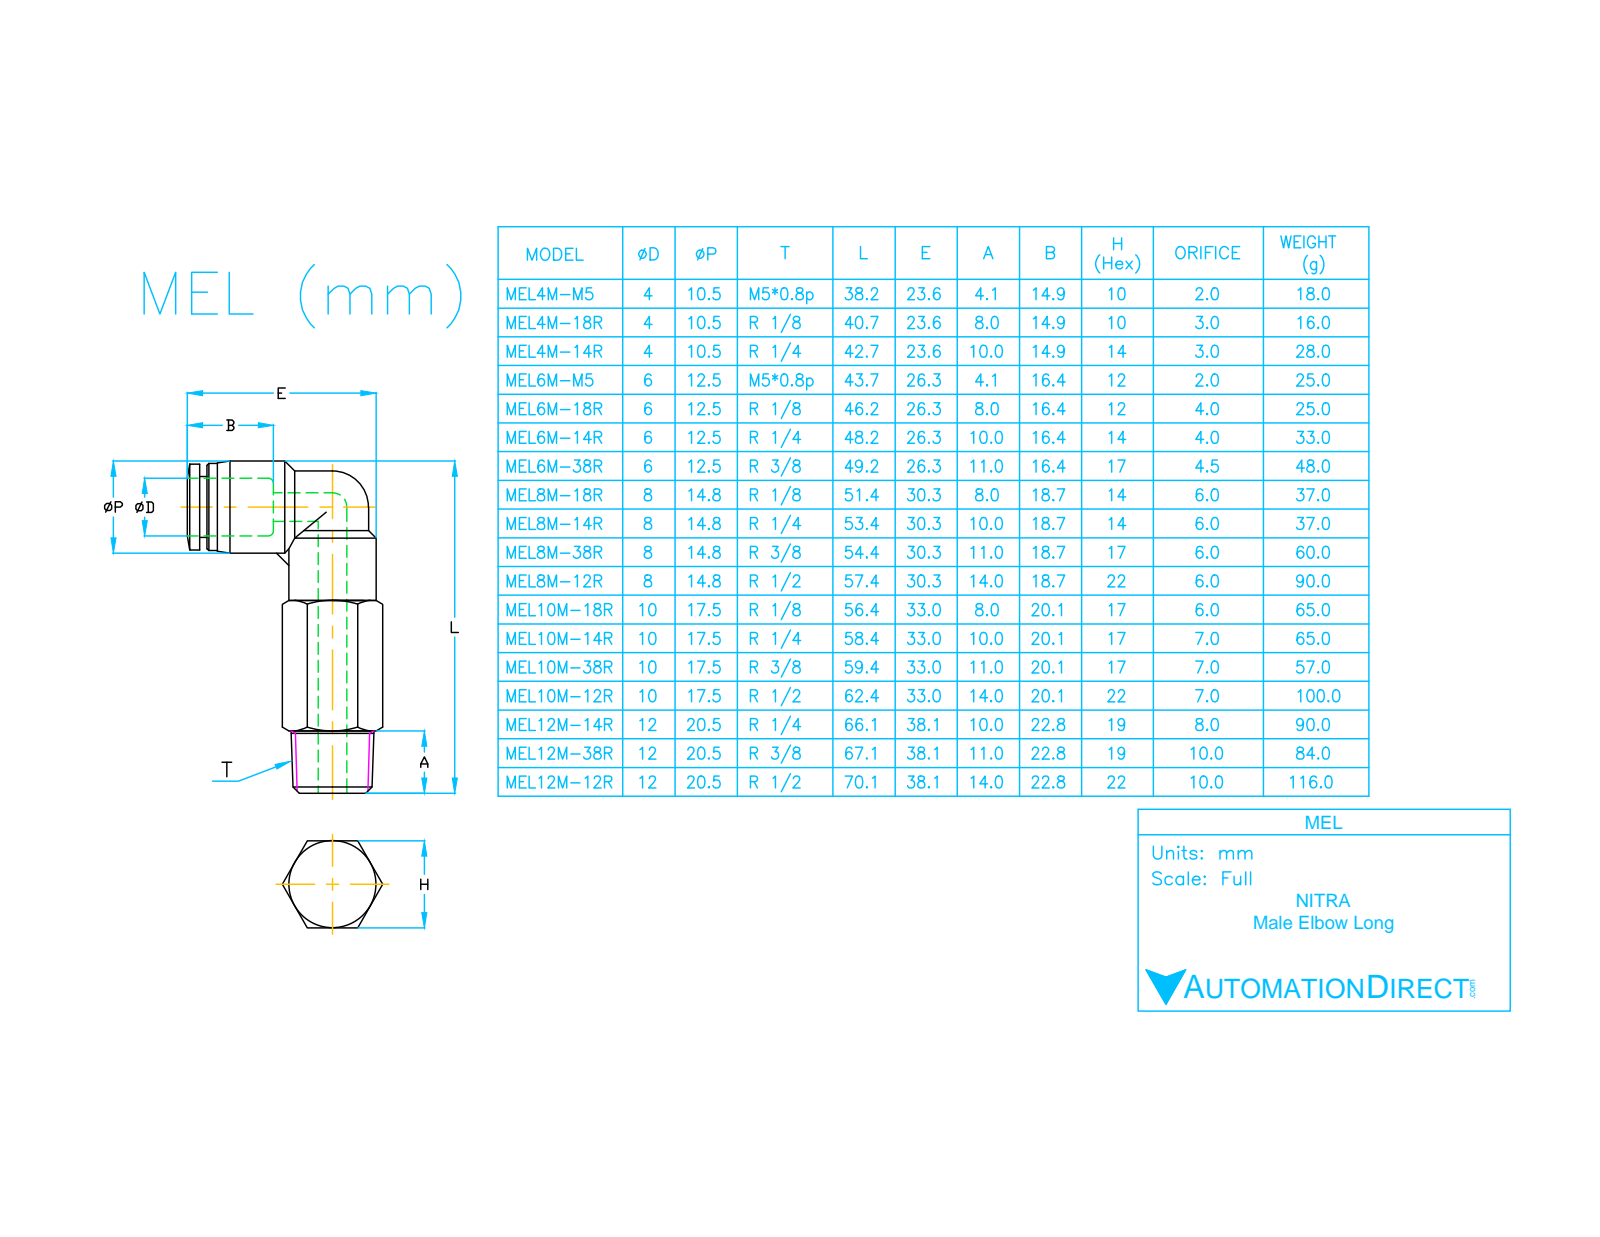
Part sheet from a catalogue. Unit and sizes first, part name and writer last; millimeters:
Units: millimetres
Overall size (bounding box): 51.4 × 31 × 14.8
Round holes (diameter × count): ⌀6 ×2, ⌀8.3 ×1
Round bosses / shafts (diameter × count): ⌀14 ×2, ⌀14.8 ×1, ⌀13.8 ×1, ⌀11.6 ×1, ⌀9.8 ×1
Partial cylindrical surfaces — rounded edges, fillets, slot ends (radius × count): R5.8 ×1
Main face-to-face distances: 14, 1.1, 8, 15.1, 16.3, 2, 18.3, 3.1, 6, 13.9
Volume: 7 060 mm³ · Surface area: 4 612 mm²
Bodies: 1 solid, 68 faces (16 planar, 19 cylindrical, 33 other)
Part name (STEP PRODUCT): MEL8M-18R
STEP written by: SolidWorks 2015 (AUTOMOTIVE_DESIGN)
